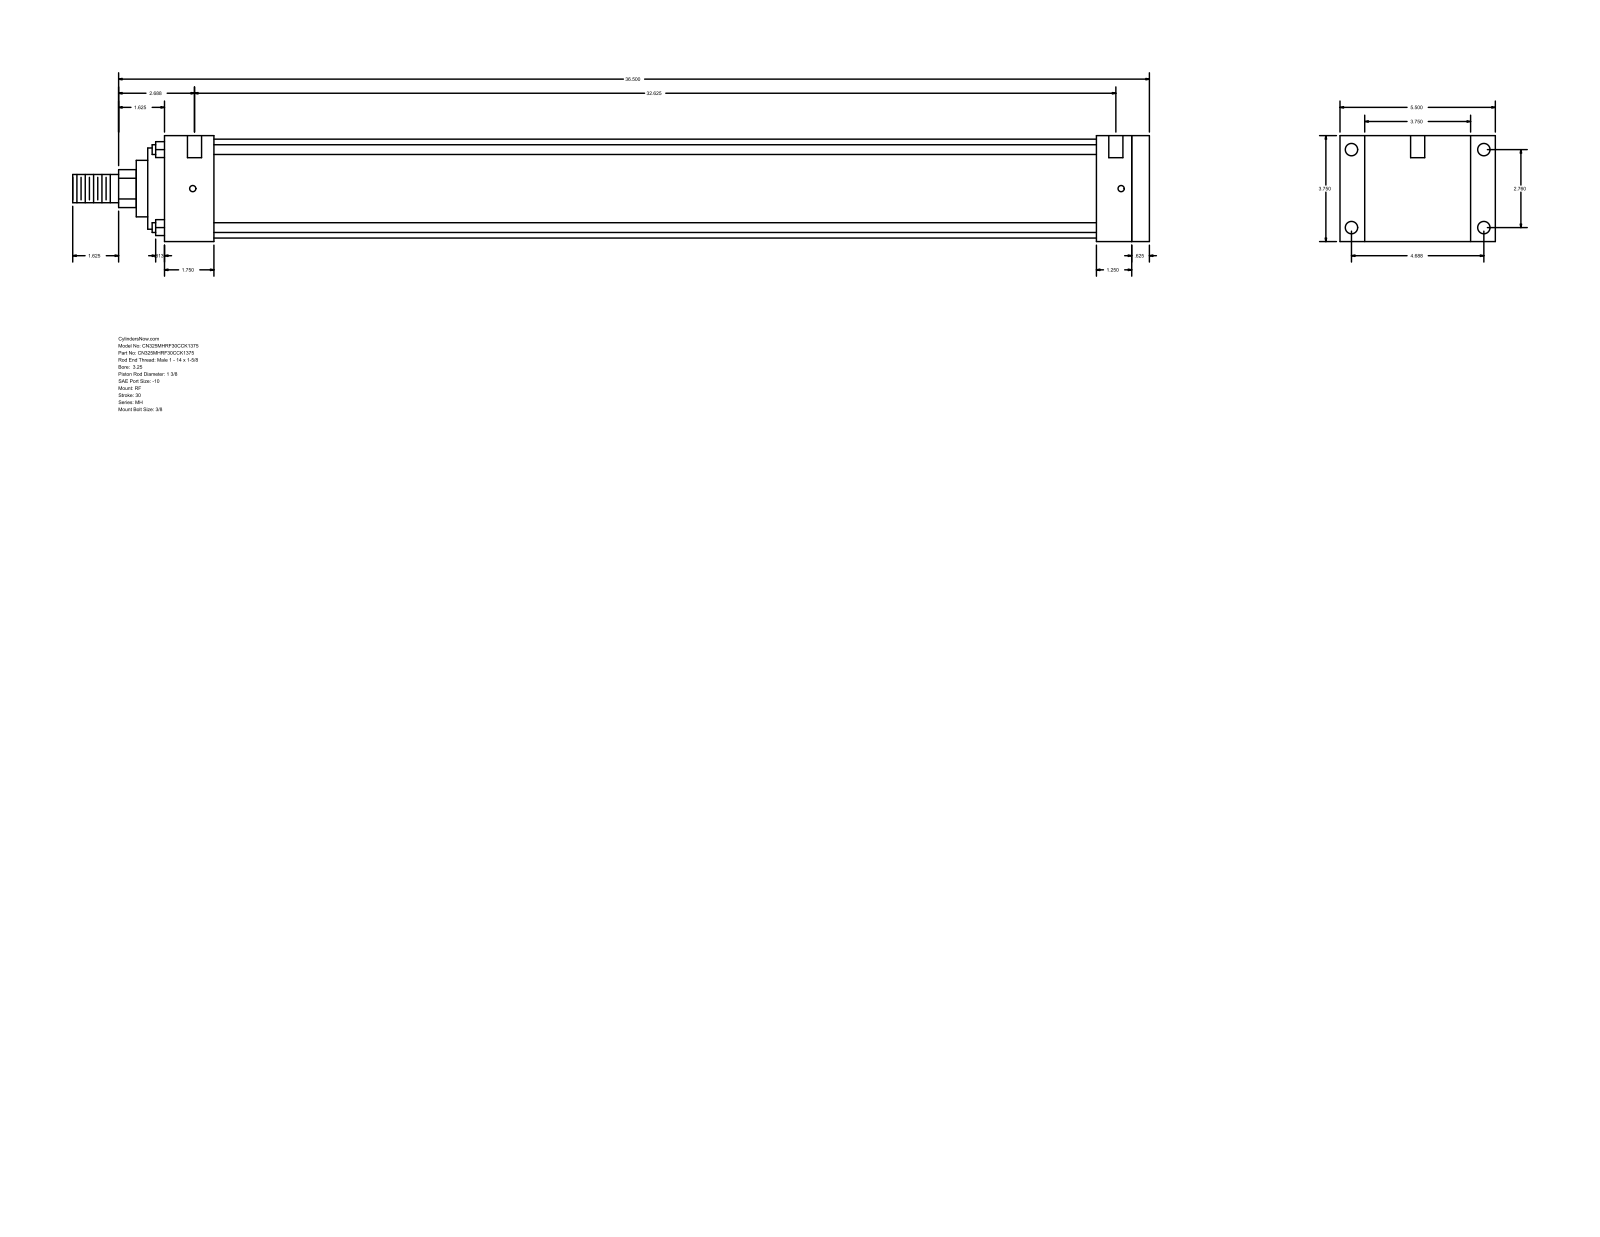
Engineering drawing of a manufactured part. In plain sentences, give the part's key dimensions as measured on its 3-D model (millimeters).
The part is named "MH_RF__0325_1.375". Its 3-D file was written by "GSSL Pune (CONFIG_CONTROL_DESIGN)". It is 0 solids with 94 faces: 65 planar, 29 cylindrical and 0 other. Overall it measures 968.38 by 139.7 by 95.25 millimeters. Round holes: 4 of diameter 5.56, 4 of diameter 11.13, 2 of diameter 12.7. Round bosses or shafts: 4 of diameter 8.76, 1 of diameter 88.9, 1 of diameter 73.03, 1 of diameter 50.8, 1 of diameter 34.92, 1 of diameter 25.4. Partial cylindrical surfaces (rounded edges, fillets, slot ends): 1 of radius 17.06. The main face-to-face distances are 95.24, 885.83, 869.96, 15.87, 22.23, 117.47, 44.45, 825.51, 841.38, 838.21. The hole center spacings are 70.1, 119.06, 138.16, 835.03, 1.59, 4.76, 828.68, 830.27.
